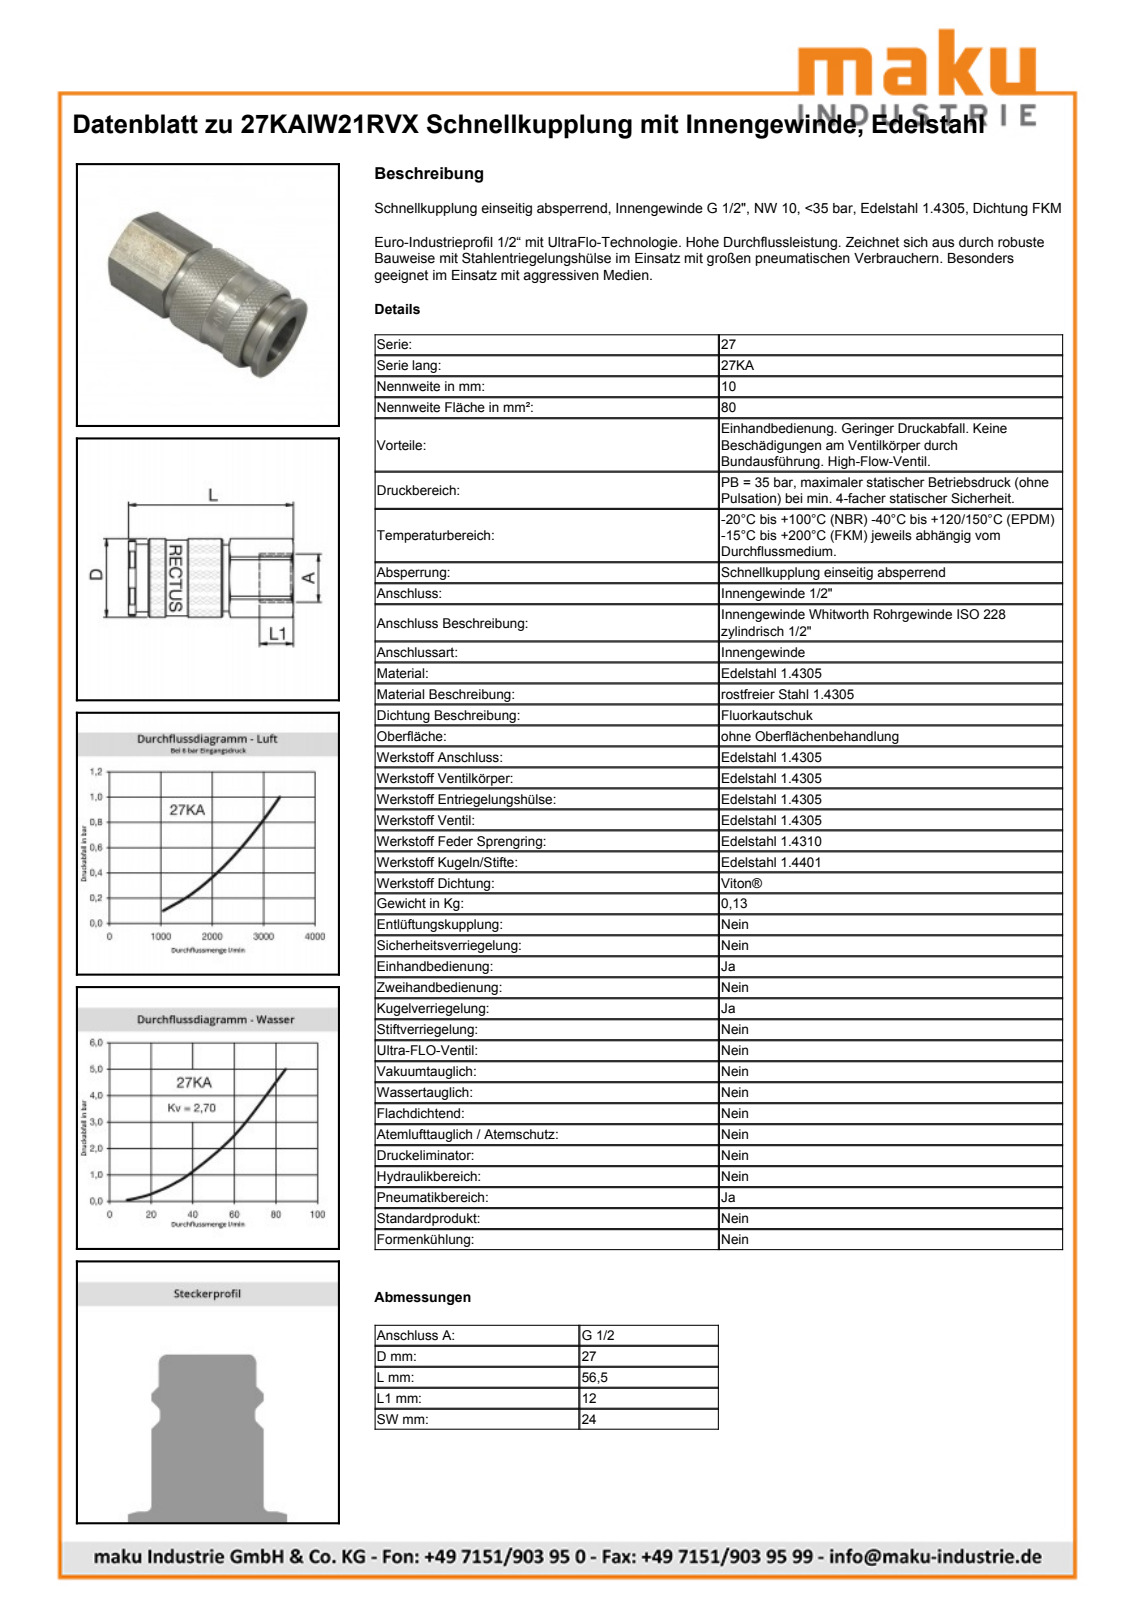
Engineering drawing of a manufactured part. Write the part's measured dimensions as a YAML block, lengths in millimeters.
part_name: "D105216"
step_written_by: "Autodesk Inventor 2011 (AUTOMOTIVE_DESIGN)"
units: millimeters
bodies: {solids: 2, faces: 822, planar: 319, cylindrical: 87, other: 416}
overall_size: [56.5, 27.15, 27.15]
volume: 23808
surface_area: 10630
round_holes:
  - {diameter: 20.3, count: 1}
  - {diameter: 20.95, count: 1}
  - {diameter: 20.96, count: 1}
  - {diameter: 23.35, count: 1}
  - {diameter: 23.55, count: 1}
round_bosses_or_shafts:
  - {diameter: 27.15, count: 1}
  - {diameter: 26, count: 1}
  - {diameter: 23.1, count: 1}
  - {diameter: 22.75, count: 1}
  - {diameter: 20, count: 1}
partial_cylinders:
  - {radius: 9.76, count: 1}
  - {radius: 12.9, count: 1}
  - {radius: 13.53, count: 1}
face_to_face_distances: [24, 31.75, 6.25, 25.5, 25, 2.5, 3.75, 29.25, 16.75, 14.25]
